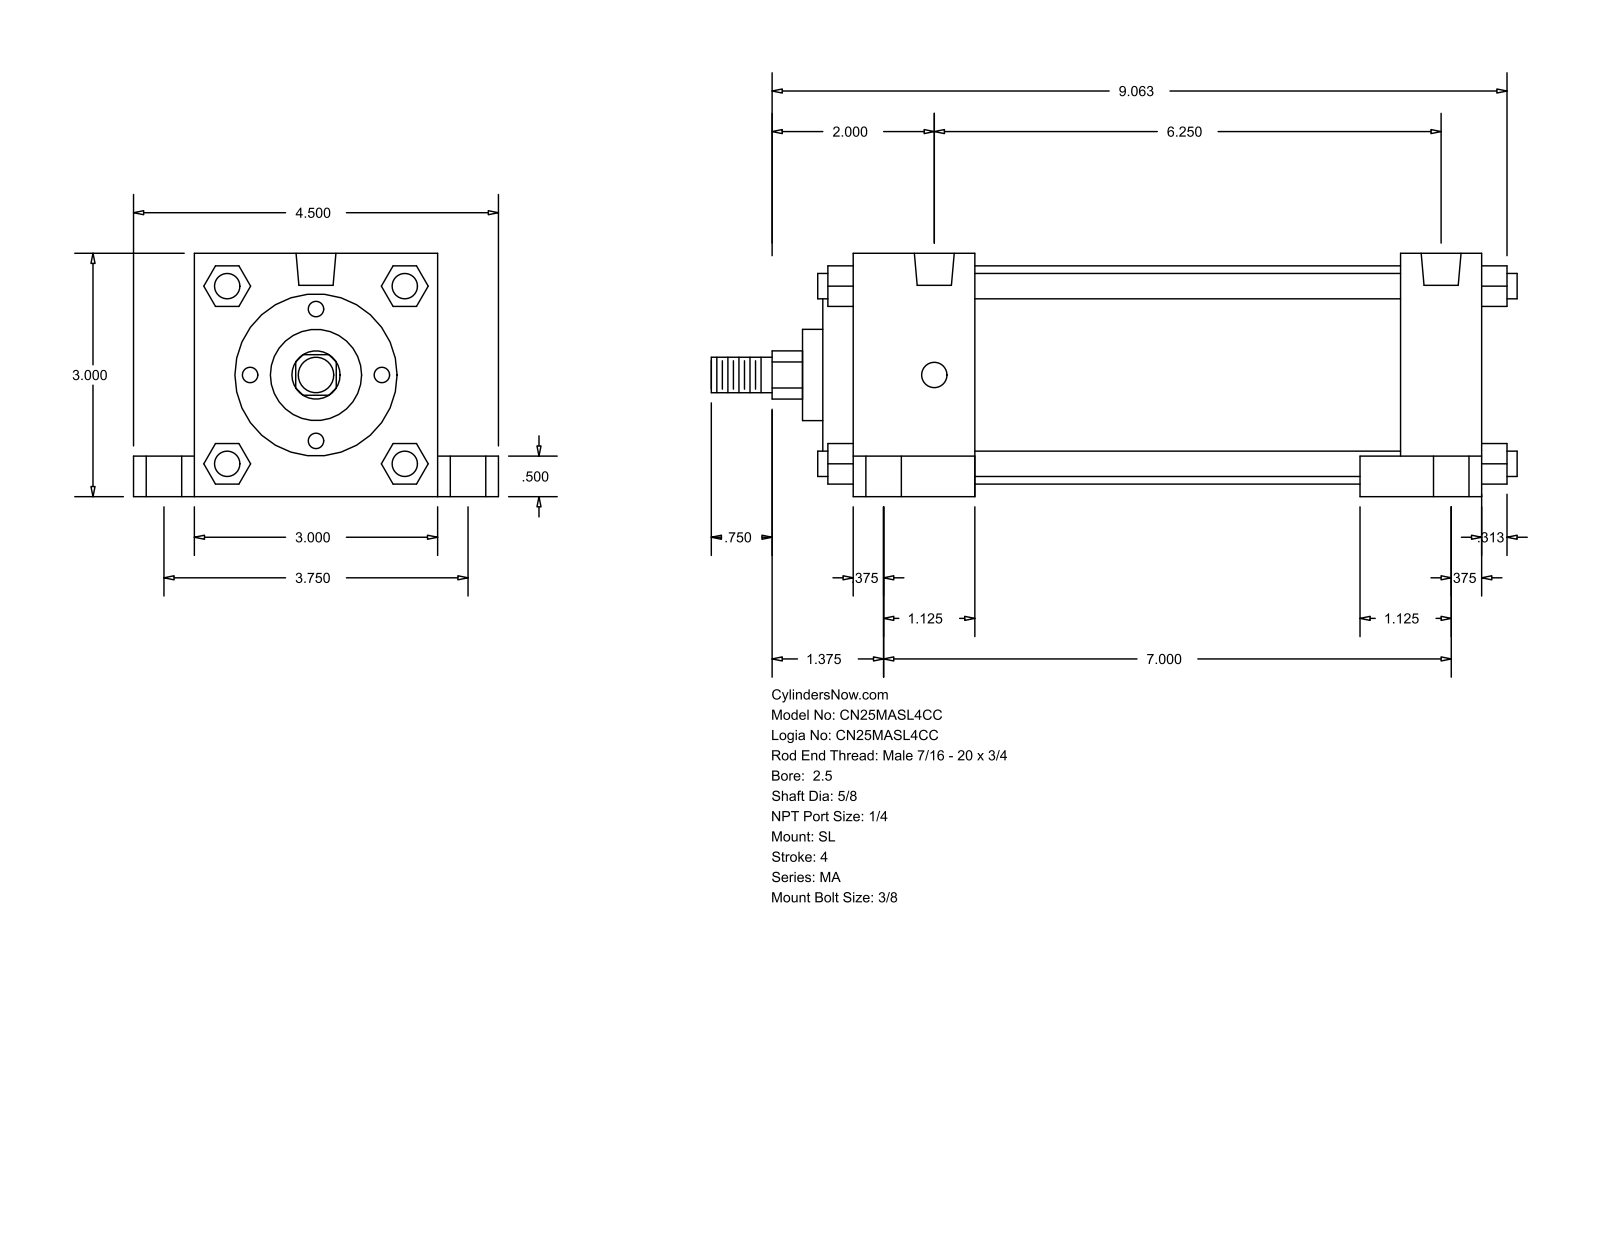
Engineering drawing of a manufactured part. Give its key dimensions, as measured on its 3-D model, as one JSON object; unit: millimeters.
{"part_name": "MA_SL__0250_0.625", "step_written_by": "GSSL Pune (CONFIG_CONTROL_DESIGN)", "units": "millimeters", "bodies": {"solids": 0, "faces": 150, "planar": 113, "cylindrical": 37, "other": 0}, "overall_size": [252.41, 114.3, 76.2], "round_holes": [[7.94, 4], [11.11, 4], [17.46, 4], [12.49, 2]], "round_bosses_or_shafts": [[7.94, 4], [68.33, 1], [50.8, 1], [28.57, 1], [15.88, 1], [11.11, 1]], "partial_cylinders_radius": [[7.54, 1]], "face_to_face_distances": [76.2, 196.85, 12.7, 133.35, 25.4, 38.1, 158.75, 171.45, 19.05, 63.5], "hole_center_spacings": [47.73, 50.2, 95.24, 158.75, 168.78, 177.8, 181.01, 201.7]}
